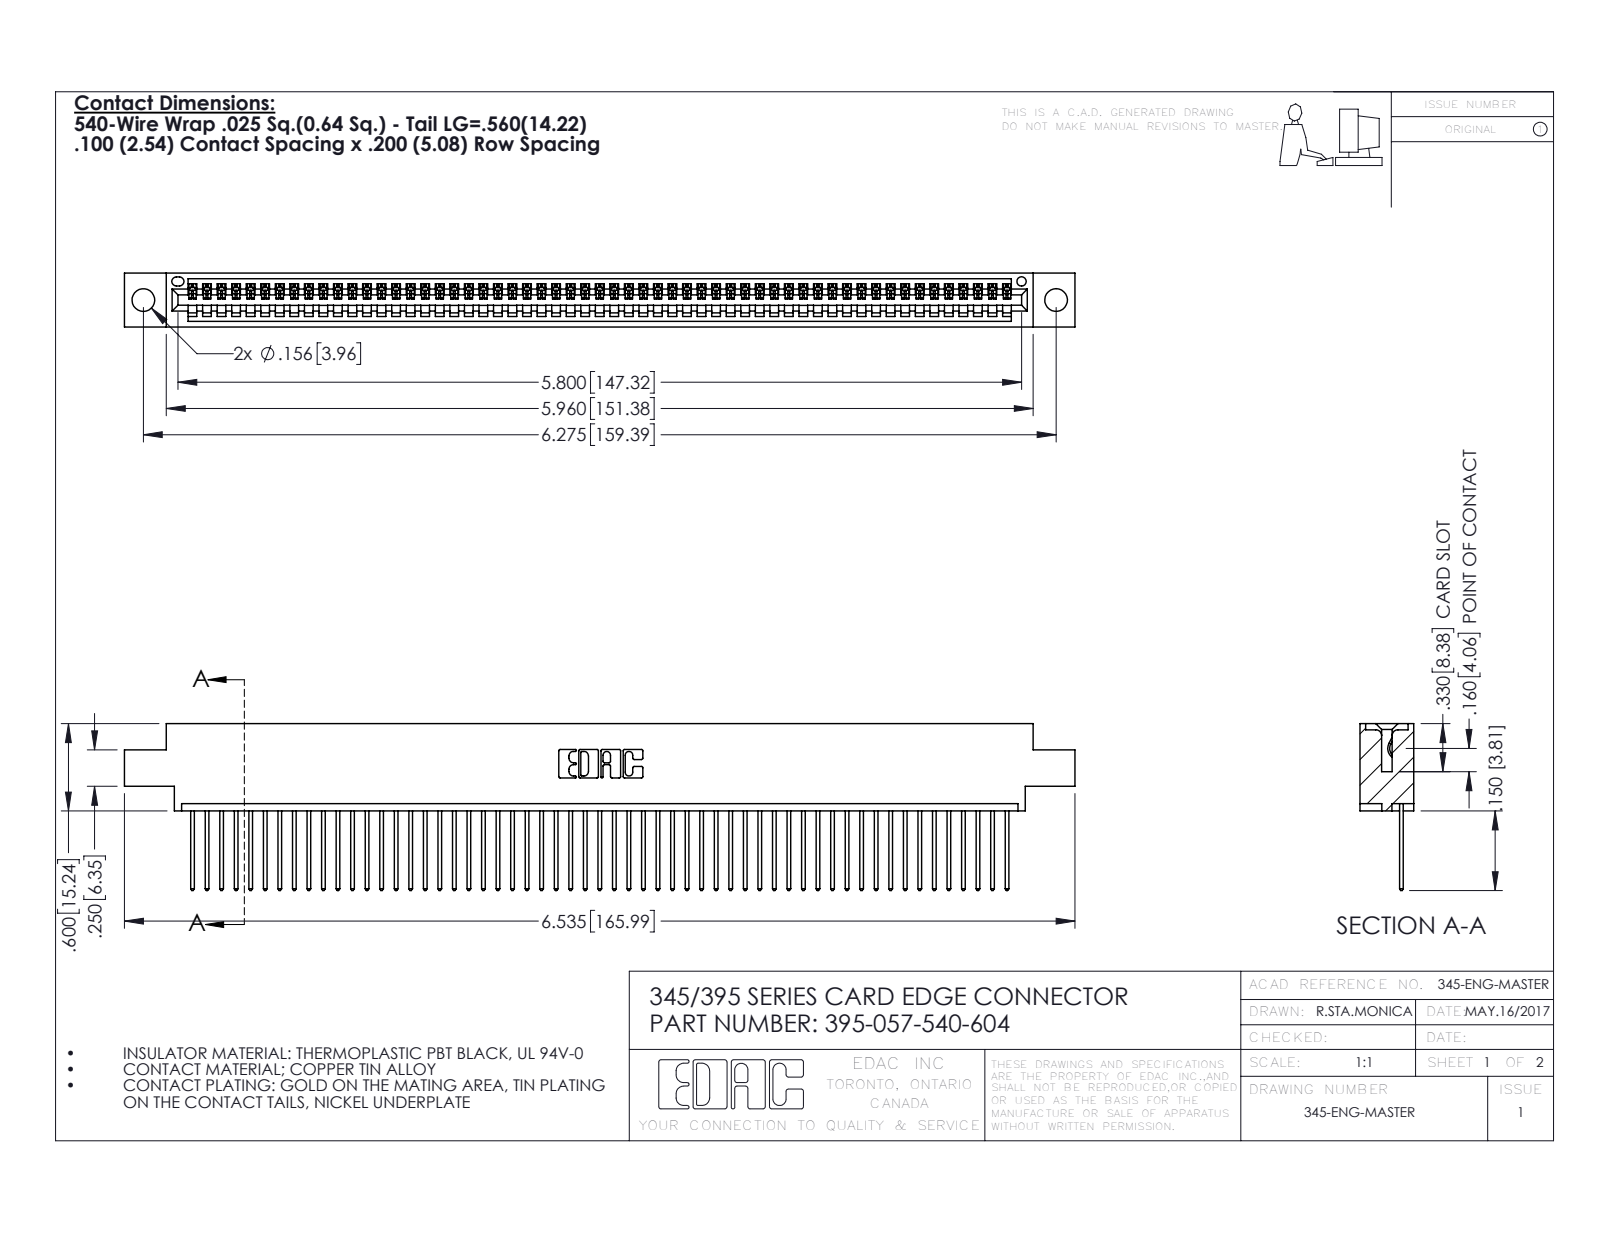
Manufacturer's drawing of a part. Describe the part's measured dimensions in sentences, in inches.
The part is named "395-057-540-604; 345-292-001_345-293-140; 345 Part_0.170 Offset - 0.156 Dia-TH". Its 3-D file was written by "SolidWorks 2016 (CONFIG_CONTROL_DESIGN)". It is 58 solids with 3436 faces: 2364 planar, 1072 cylindrical and 0 other. Overall it measures 6.535 by 1.147 by 0.37 inches. Its volume is 0.962 cubic inches and its surface area 33.55 square inches. Round holes: 2 of diameter 0.156, 1 of diameter 0.064. Partial cylindrical surfaces (rounded edges, fillets, slot ends): 114 of radius 0.006, 114 of radius 0.01, 22 of radius 0.01, 6 of radius 0.007, 6 of radius 0.031, 3 of radius 0.026, 2 of radius 0.031, 2 of radius 0.04. The main face-to-face distances are 0.298, 0.072, 0.37, 0.098, 0.272, 0.025, 0.2, 0.225, 0.175, 0.149. The hole center spacings are 0.27, 6.039, 6.275.
